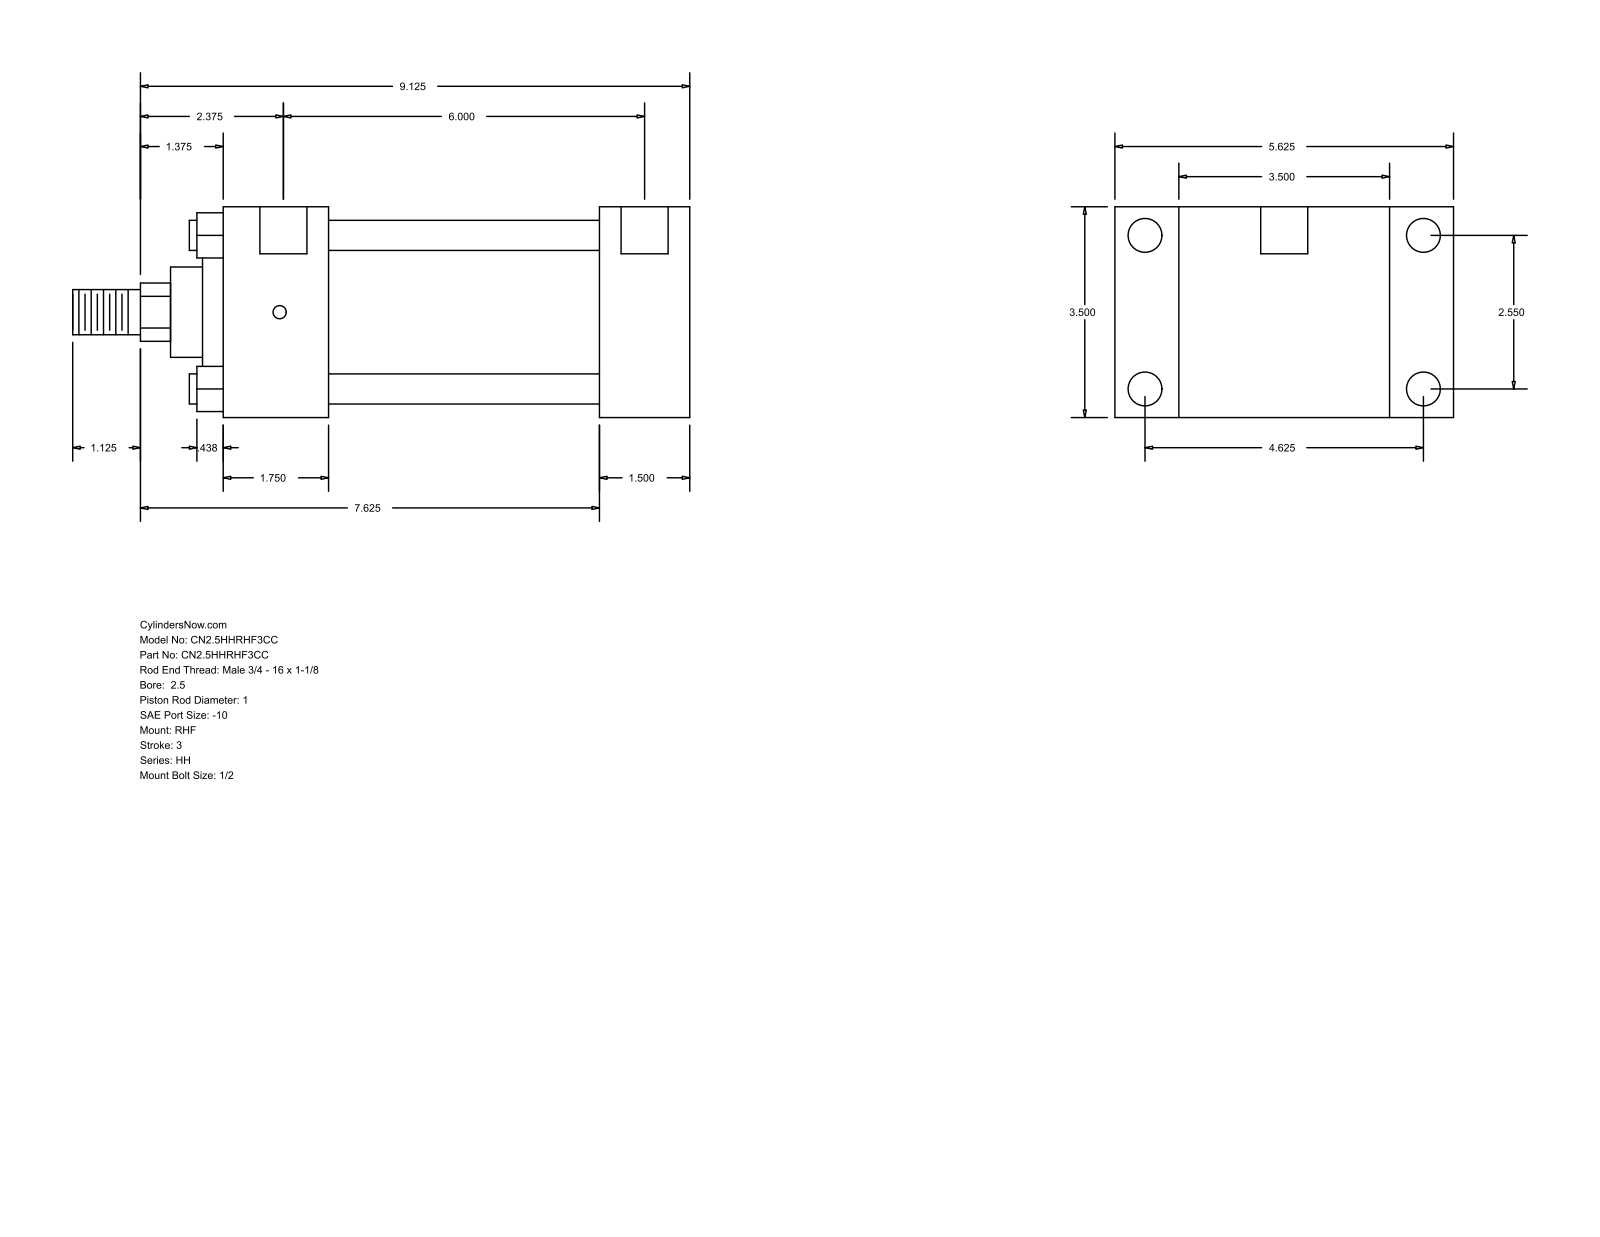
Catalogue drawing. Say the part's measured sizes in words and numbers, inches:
The part is named "HH_RHF__0250_1". Its 3-D file was written by "GSSL Pune (CONFIG_CONTROL_DESIGN)". It is 0 solids with 90 faces: 61 planar, 29 cylindrical and 0 other. Overall it measures 10.25 by 5.625 by 3.5 inches. Round holes: 4 of diameter 0.219, 4 of diameter 0.563, 2 of diameter 0.781. Round bosses or shafts: 4 of diameter 0.5, 1 of diameter 2.875, 1 of diameter 2.375, 1 of diameter 1.5, 1 of diameter 1, 1 of diameter 0.75. Partial cylindrical surfaces (rounded edges, fillets, slot ends): 1 of radius 0.484. The main face-to-face distances are 3.5, 1.5, 1.063, 4.563, 6.25, 7.75, 5.625, 1.75, 4.5, 6. The hole center spacings are 0.063, 2.55, 4.625, 5.281, 6.062, 6.125, 6.
